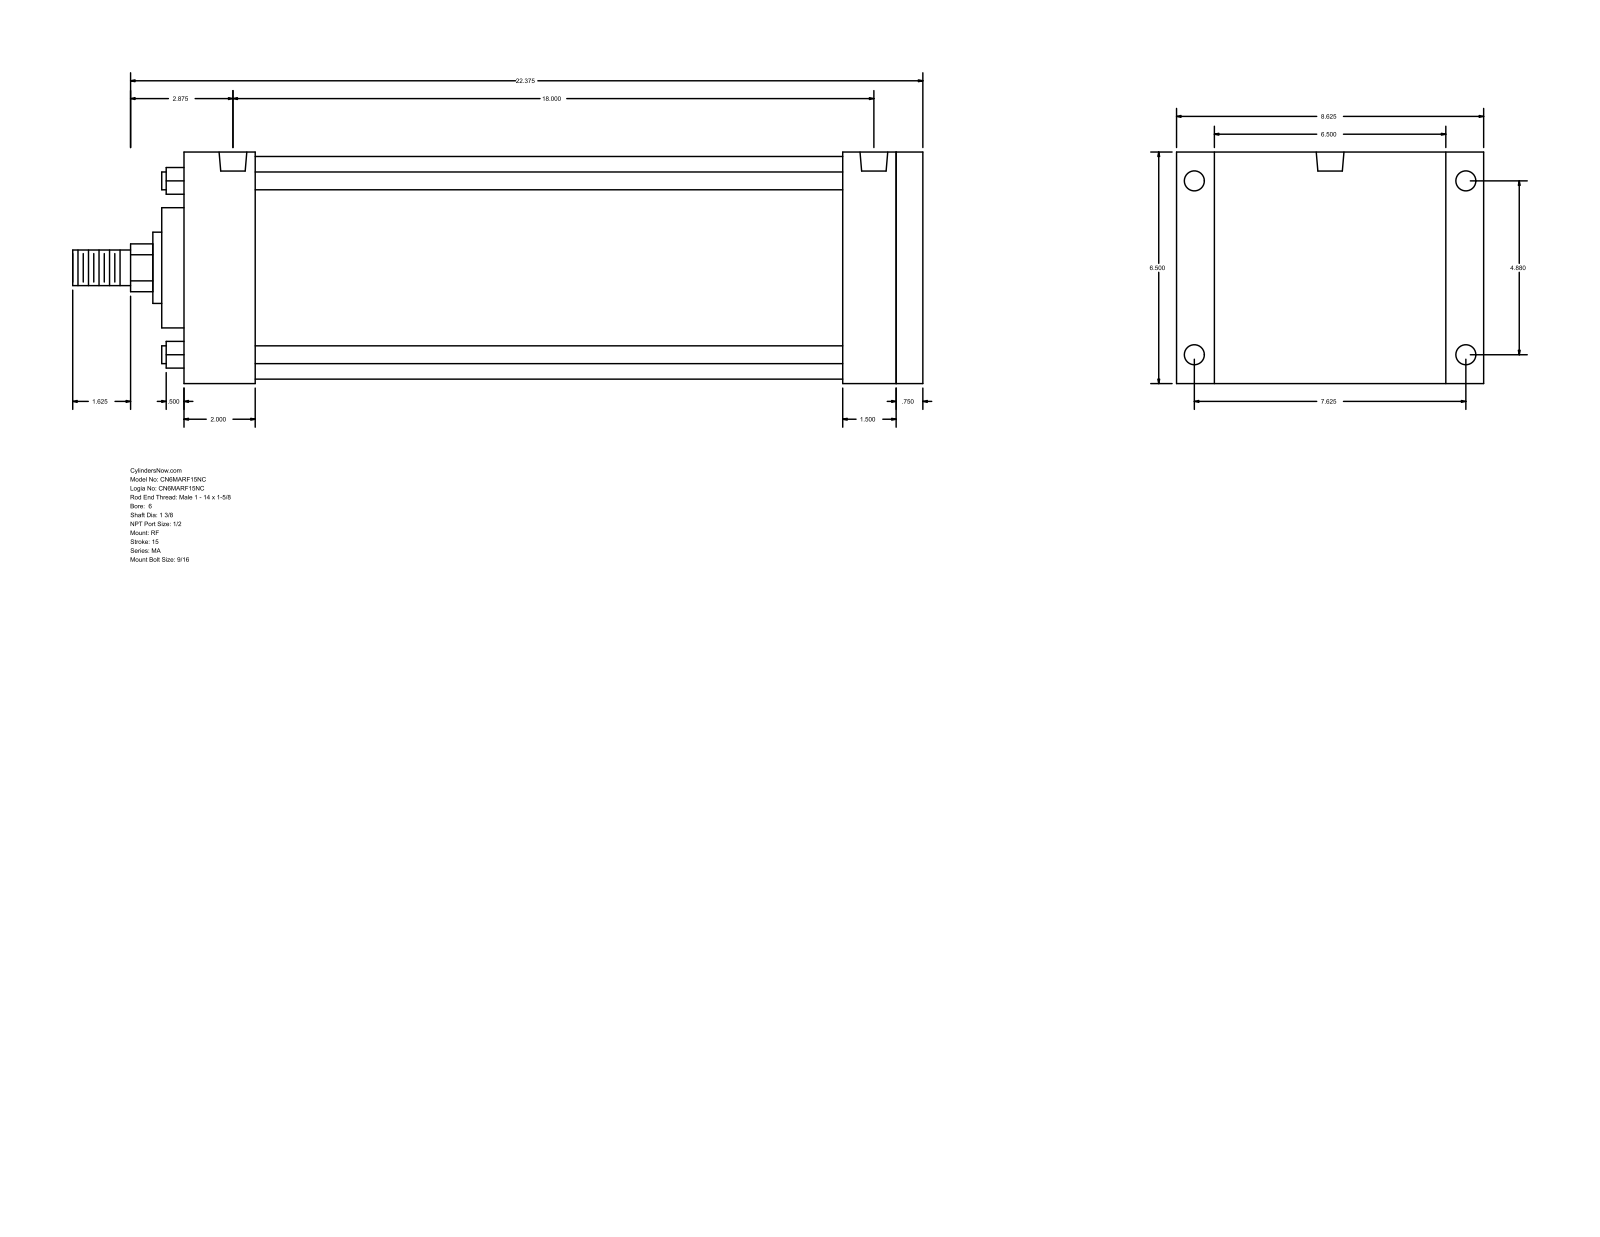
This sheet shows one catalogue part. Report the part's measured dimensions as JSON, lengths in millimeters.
{"part_name": "MA_RF__0600_1.375", "step_written_by": "GSSL Pune (CONFIG_CONTROL_DESIGN)", "units": "millimeters", "bodies": {"solids": 0, "faces": 94, "planar": 65, "cylindrical": 29, "other": 0}, "overall_size": [609.6, 219.07, 165.1], "round_holes": [[14.29, 4], [17.46, 4], [19.77, 2]], "round_bosses_or_shafts": [[12.7, 4], [158.75, 1], [85.72, 1], [50.8, 1], [34.92, 1], [25.4, 1]], "partial_cylinders_radius": [[17.06, 1]], "face_to_face_distances": [165.1, 530.23, 511.17, 19.06, 57.15, 50.8, 460.37, 479.43, 473.08, 422.28], "hole_center_spacings": [123.96, 193.68, 229.95, 460.38, 3.18, 457.2]}
